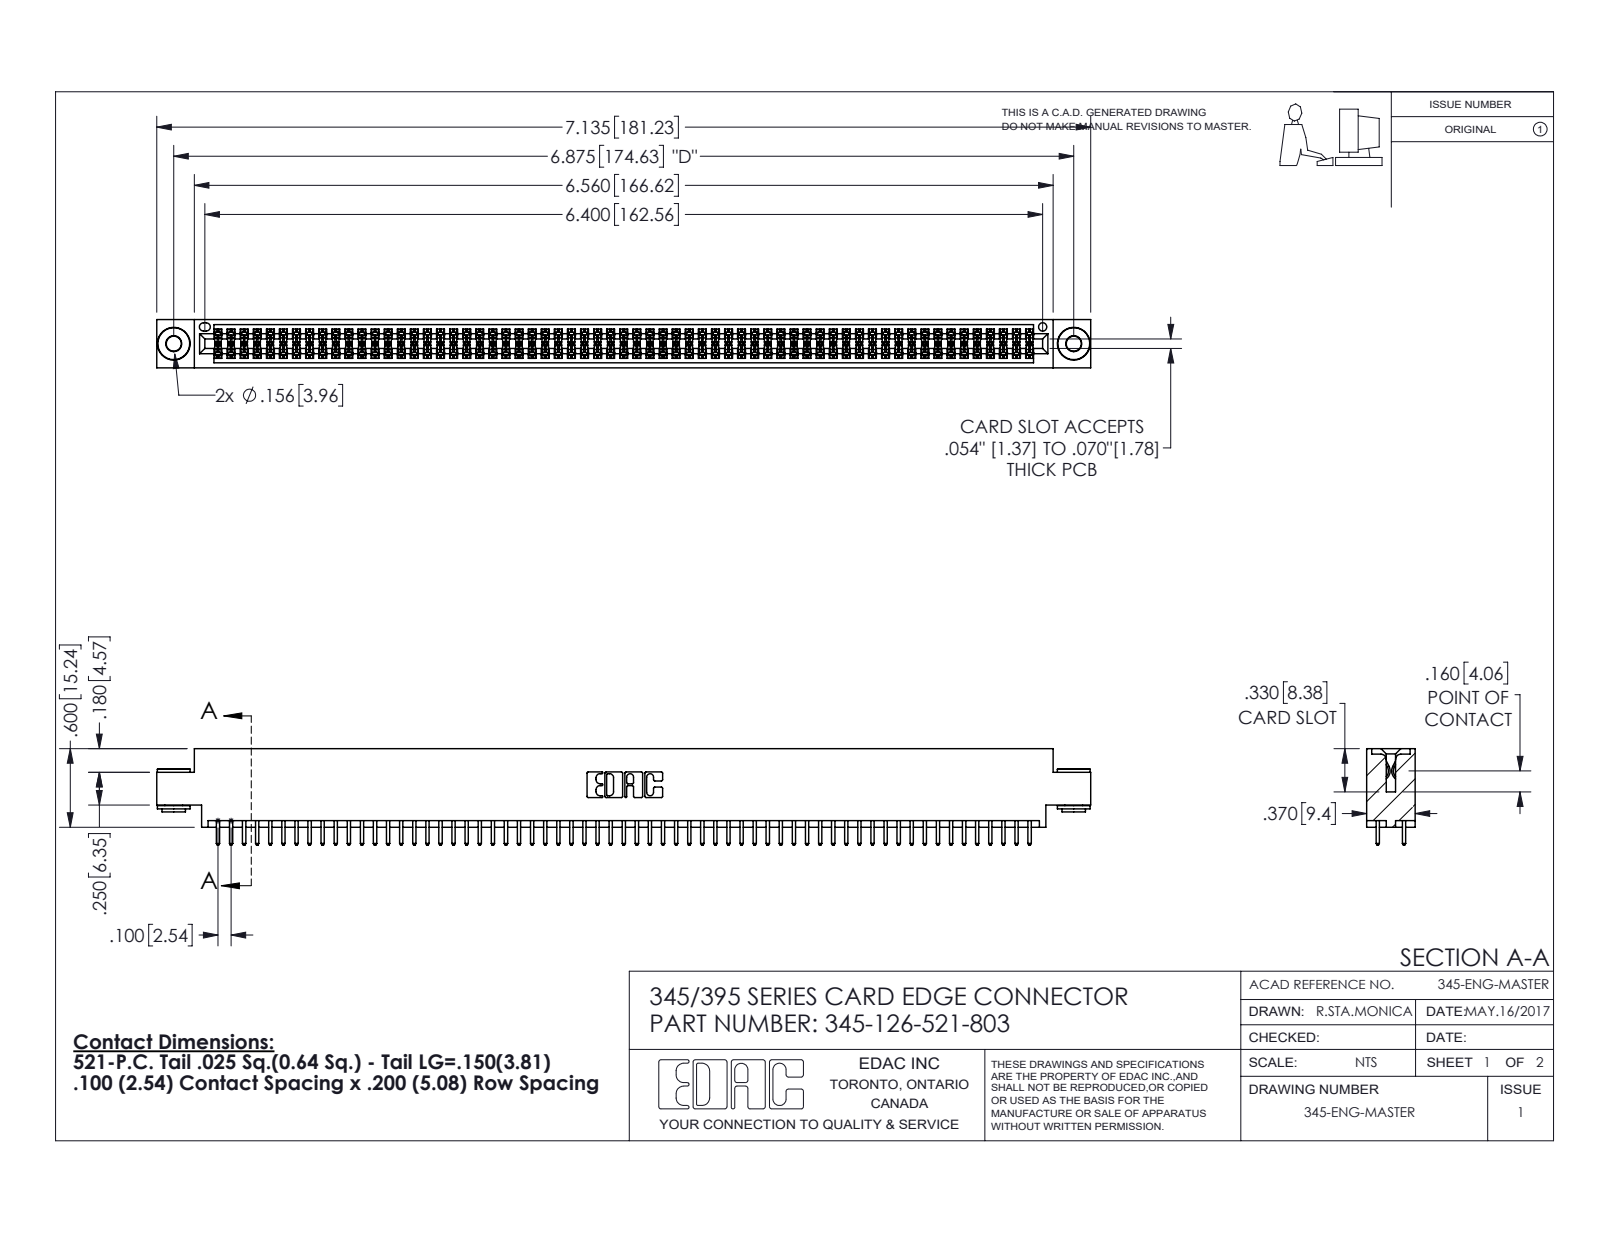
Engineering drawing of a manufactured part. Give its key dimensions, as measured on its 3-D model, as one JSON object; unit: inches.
{"part_name": "345-292-001_345-293-121; 345-126-521-803; 345-250-002_345-250-002-102; 345 Part_0.170 Offset - 0.156 Dia-TH", "step_written_by": "SolidWorks 2016 (CONFIG_CONTROL_DESIGN)", "units": "inches", "bodies": {"solids": 129, "faces": 6468, "planar": 4252, "cylindrical": 2208, "other": 8}, "overall_size": [7.135, 0.737, 0.37], "volume_in3": 1.077, "surface_area_in2": 41.1, "round_holes": [[0.116, 2], [0.156, 2], [0.064, 1]], "round_bosses_or_shafts": [[0.25, 2], [0.18, 2], [0.136, 2]], "partial_cylinders_radius": [[0.006, 189], [0.01, 126], [0.01, 22], [0.007, 6], [0.031, 6], [0.026, 3], [0.014, 2], [0.019, 2]], "face_to_face_distances": [0.072, 0.298, 0.2, 0.37, 0.098, 0.272, 0.025, 0.225, 0.175, 0.149], "hole_center_spacings": [0.27, 6.639, 6.875]}
